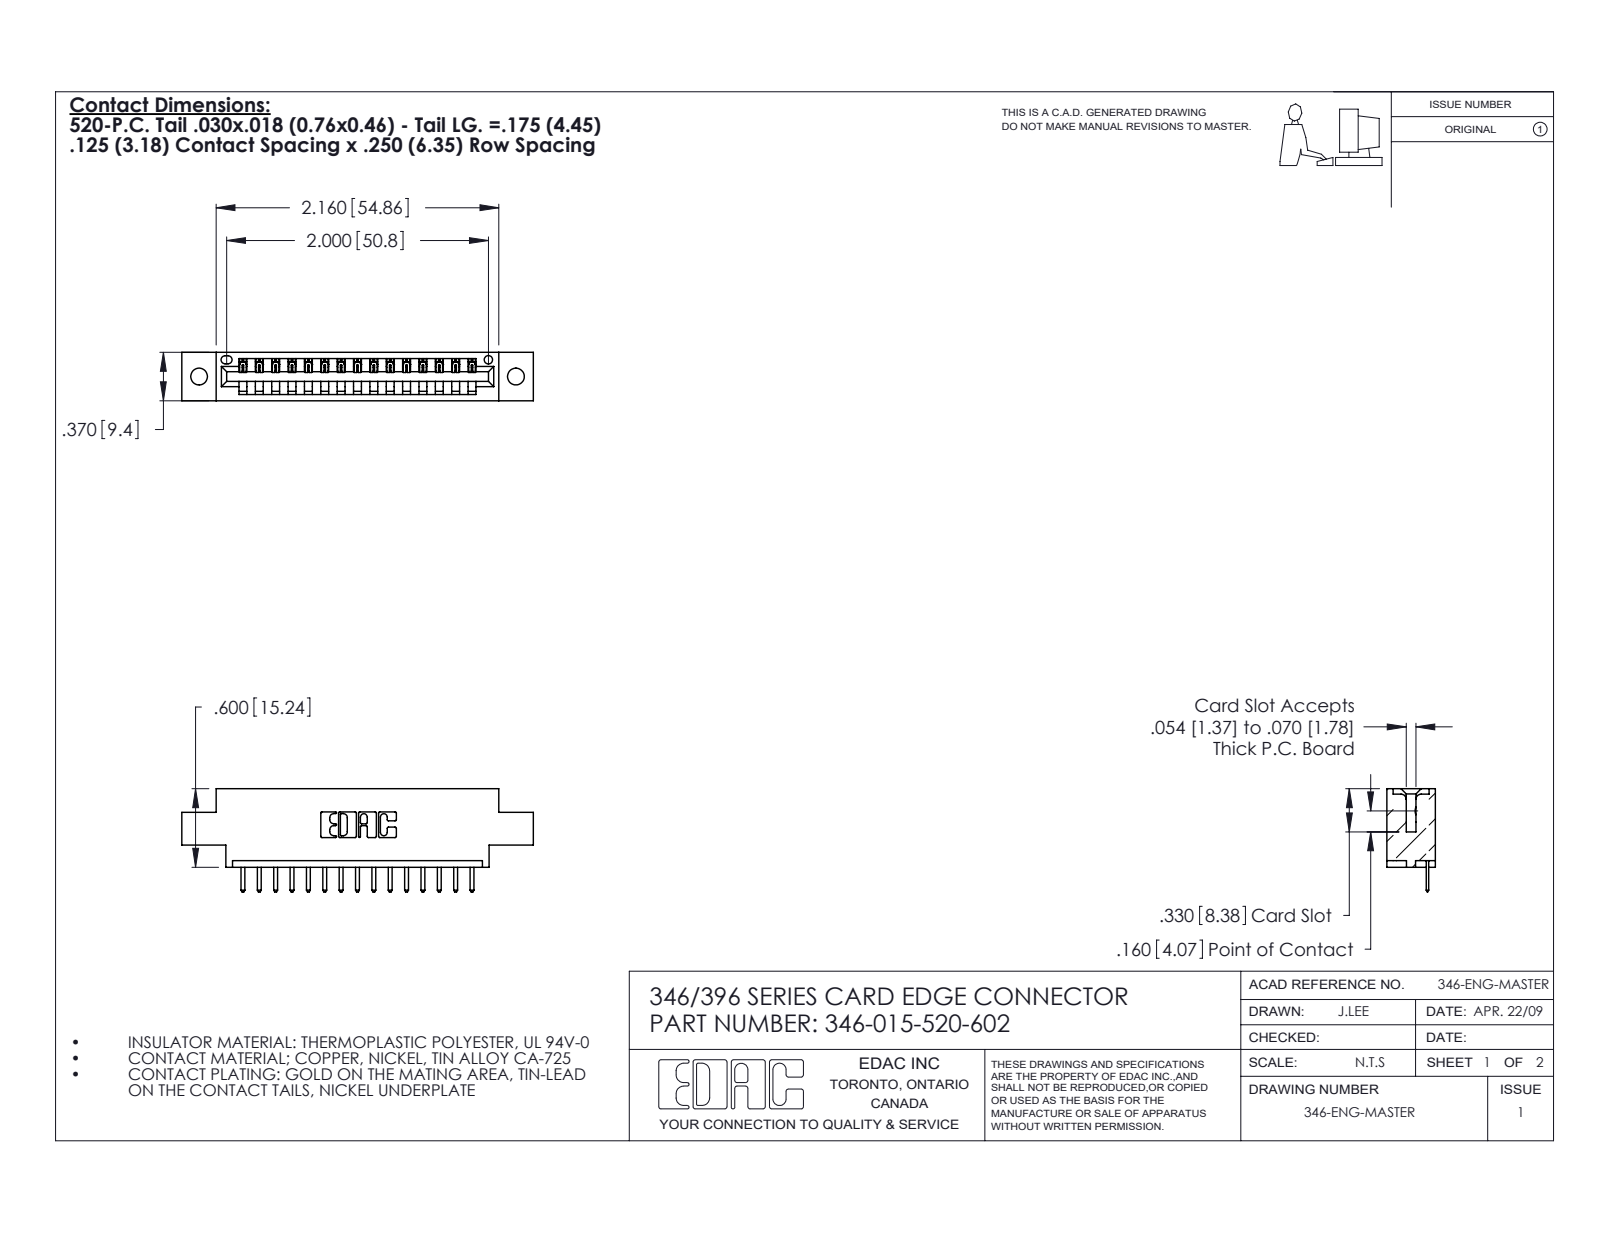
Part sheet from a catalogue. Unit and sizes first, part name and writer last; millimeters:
Units: millimetres
Overall size (bounding box): 68.2 × 20 × 9.4
Round holes (diameter × count): ⌀3.3 ×2, ⌀1.6 ×1
Partial cylindrical surfaces — rounded edges, fillets, slot ends (radius × count): R0.3 ×32, R0.2 ×30, R0.3 ×22, R0.2 ×6, R0.8 ×6, R0.7 ×3, R0.8 ×2, R1 ×2
Main face-to-face distances: 9.4, 1.2, 8.2, 6.4, 3.8, 5.6, 2.5, 4.4, 1.8, 7.6
Hole centre spacings: 6.2, 56.2, 61.5
Volume: 6 110 mm³ · Surface area: 7 090 mm²
Bodies: 16 solids, 1056 faces (710 planar, 346 cylindrical, 0 other)
Part name (STEP PRODUCT): 345-292-001_345-293-120; 346 Part_0.170 Offset - 0.128 Dia; 346-015-520-602
STEP written by: SolidWorks 2020 (CONFIG_CONTROL_DESIGN)
